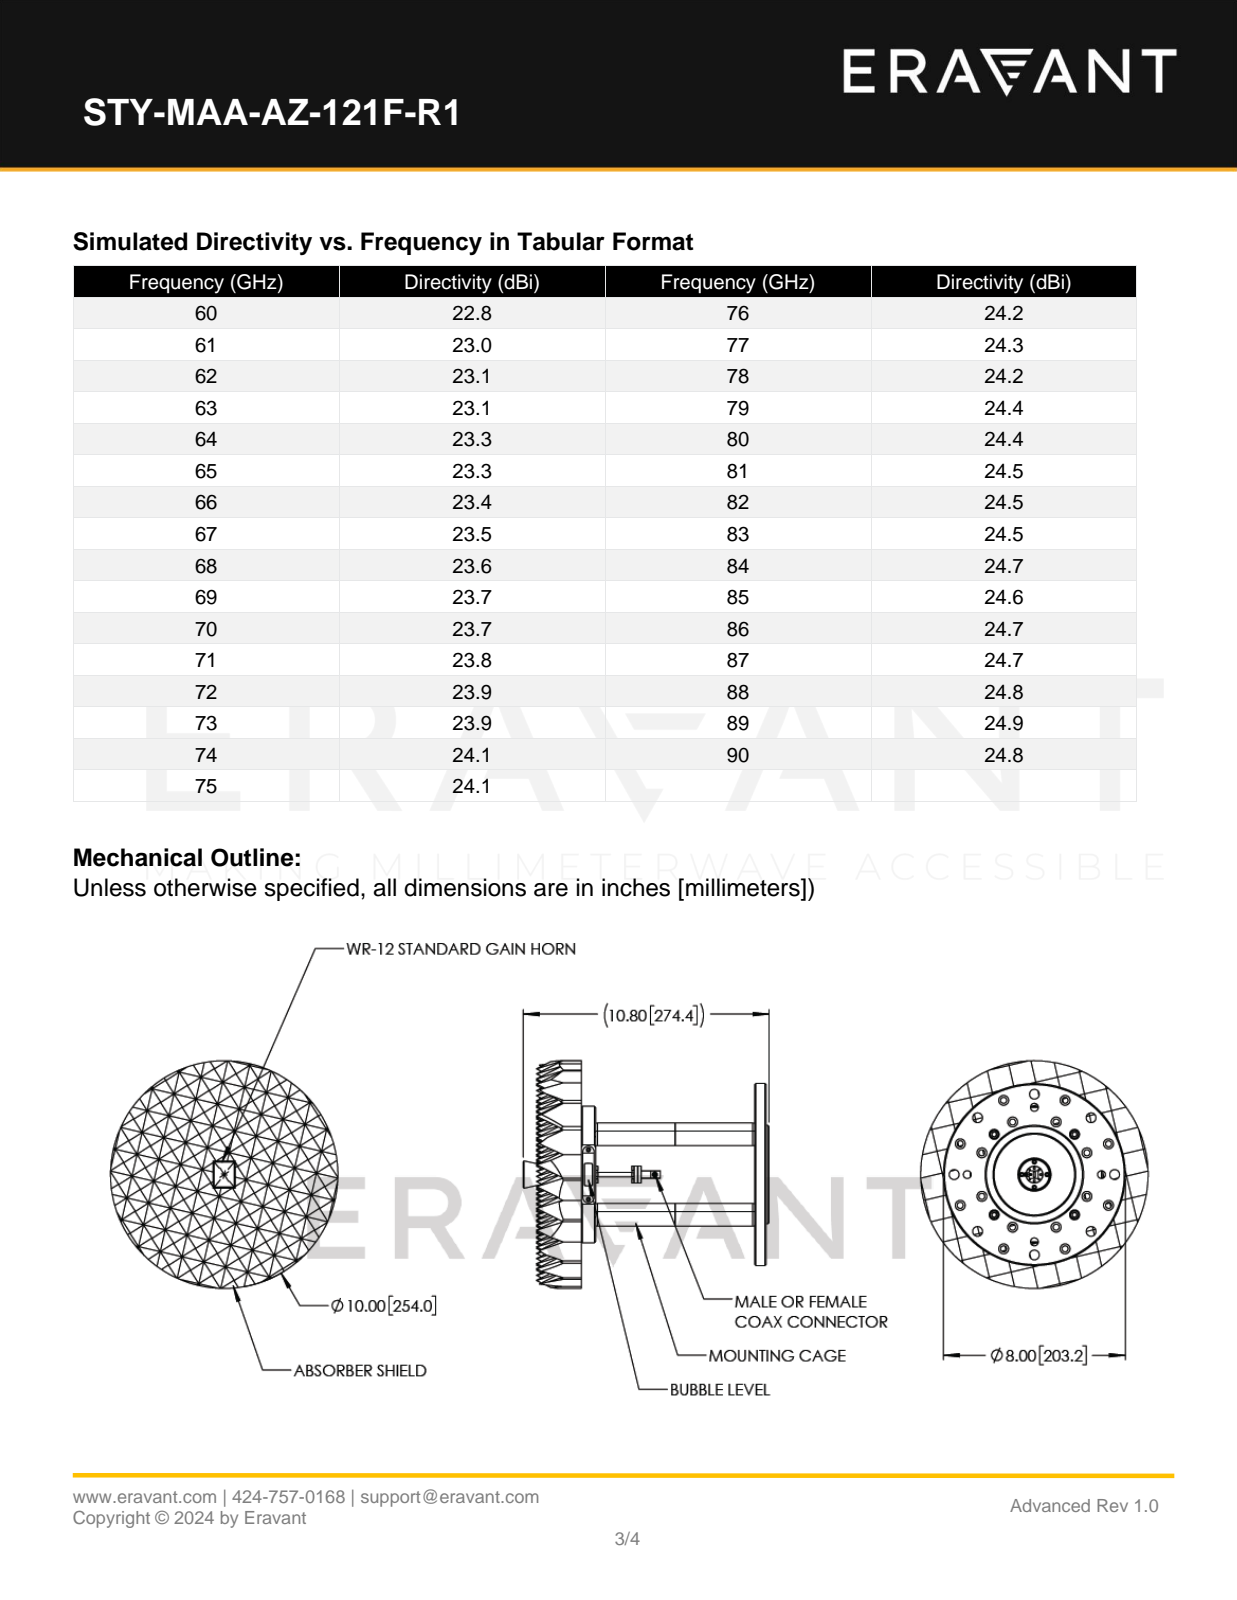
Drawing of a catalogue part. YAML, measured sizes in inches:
part_name: "STY-MAA-AZ-121F-R1"
step_written_by: "SolidWorks 2021 (CONFIG_CONTROL_DESIGN)"
units: inches
bodies: {solids: 88, faces: 1485, planar: 661, cylindrical: 345, other: 479}
overall_size: [10.802, 10, 10]
volume: 152.1
surface_area: 789.5
round_holes:
  - {diameter: 0.266, count: 20}
  - {diameter: 0.437, count: 16}
  - {diameter: 0.433, count: 8}
  - {diameter: 0.348, count: 4}
  - {diameter: 0.75, count: 4}
  - {diameter: 0.089, count: 2}
  - {diameter: 0.125, count: 2}
  - {diameter: 0.039, count: 1}
  - {diameter: 0.094, count: 1}
  - {diameter: 1.4, count: 1}
  - {diameter: 3.543, count: 1}
round_bosses_or_shafts:
  - {diameter: 1, count: 4}
  - {diameter: 0.437, count: 4}
  - {diameter: 0.18, count: 4}
  - {diameter: 10, count: 1}
  - {diameter: 8, count: 1}
  - {diameter: 6, count: 1}
  - {diameter: 4.331, count: 1}
  - {diameter: 0.75, count: 1}
partial_cylinders:
  - {radius: 0.005, count: 48}
  - {radius: 0.08, count: 2}
  - {radius: 0.25, count: 2}
  - {radius: 0.005, count: 1}
  - {radius: 0.24, count: 1}
face_to_face_distances: [0.984, 1.969, 0.985, 1.969, 2.953, 2.953, 3.937, 0.984, 4.922, 3.937]
hole_center_spacings: [4.326, 5.585, 3.458, 5.046, 5.918, 1.551, 2.496, 3.53]
